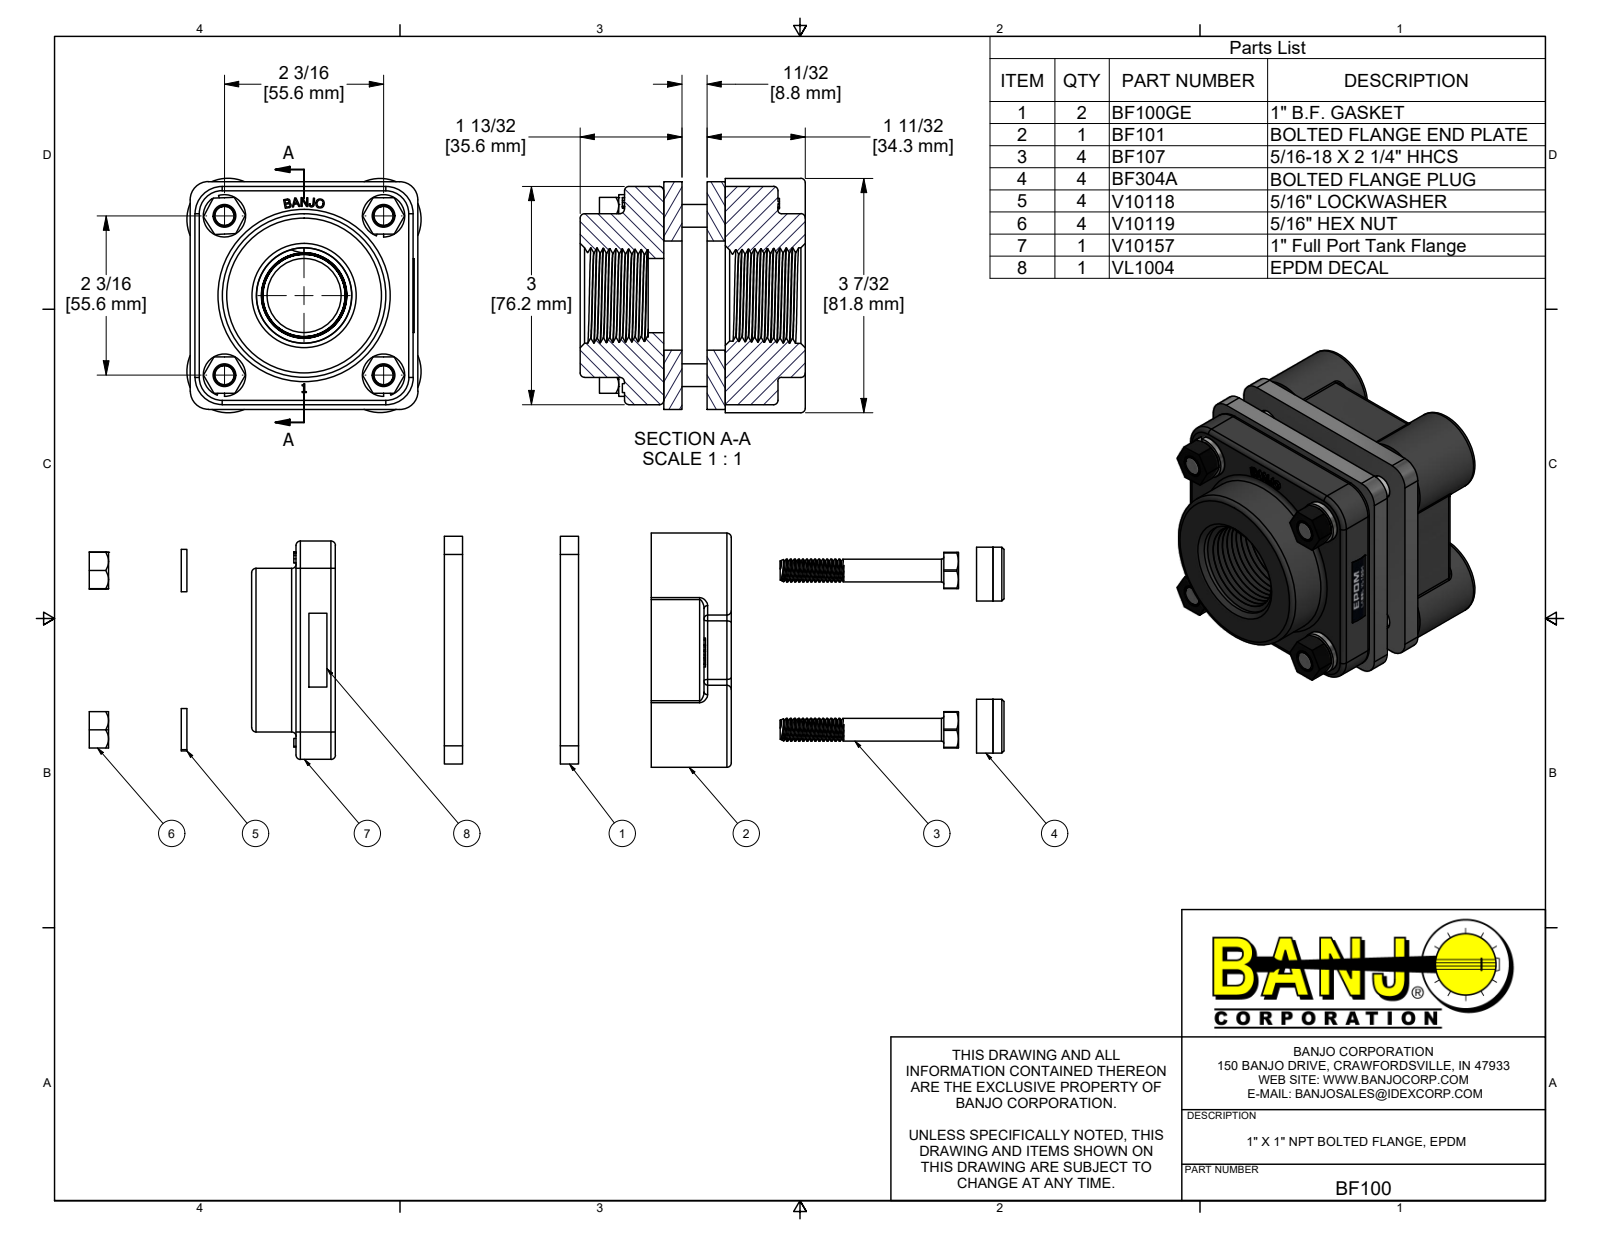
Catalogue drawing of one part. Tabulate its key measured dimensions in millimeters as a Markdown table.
| quantity | value |
| --- | --- |
| part name | BF100; BF101; BF107; BF304A (+5 more) |
| STEP written by | Autodesk Inventor 2019 (AUTOMOTIVE_DESIGN) |
| units | millimeters |
| bodies | 21 solids, 1308 faces (490 planar, 322 cylindrical, 496 other) |
| overall size | 534.4 × 81.8 × 81.8 |
| volume | 302 300 mm³ |
| surface area | 148 100 mm² |
| round holes (diameter × count) | 6.4 × 4, 8.2 × 4, 8.6 × 4, 8.7 × 4, 8.9 × 4, 18.3 × 4, 18.9 × 4, 25.9 × 1, 38.1 × 1 |
| round bosses / shafts (diameter × count) | 6.8 × 60, 18.8 × 4, 14.8 × 4, 8 × 4, 57.2 × 1 |
| partial cylindrical surfaces (radius × count) | 1.5 × 20, 1.3 × 8, 3.4 × 8, 6.4 × 4, 7.2 × 4, 9.5 × 4, 14.4 × 4, 9.5 × 1 |
| main face-to-face distances | 6.4, 15.1, 21.5, 8.8, 1.7, 77.9, 43.1, 27.9, 63.1, 34.3 |
| hole center spacings | 54.3, 54.5, 55.7, 1.8, 2, 37.5, 39.3, 39.5 |
